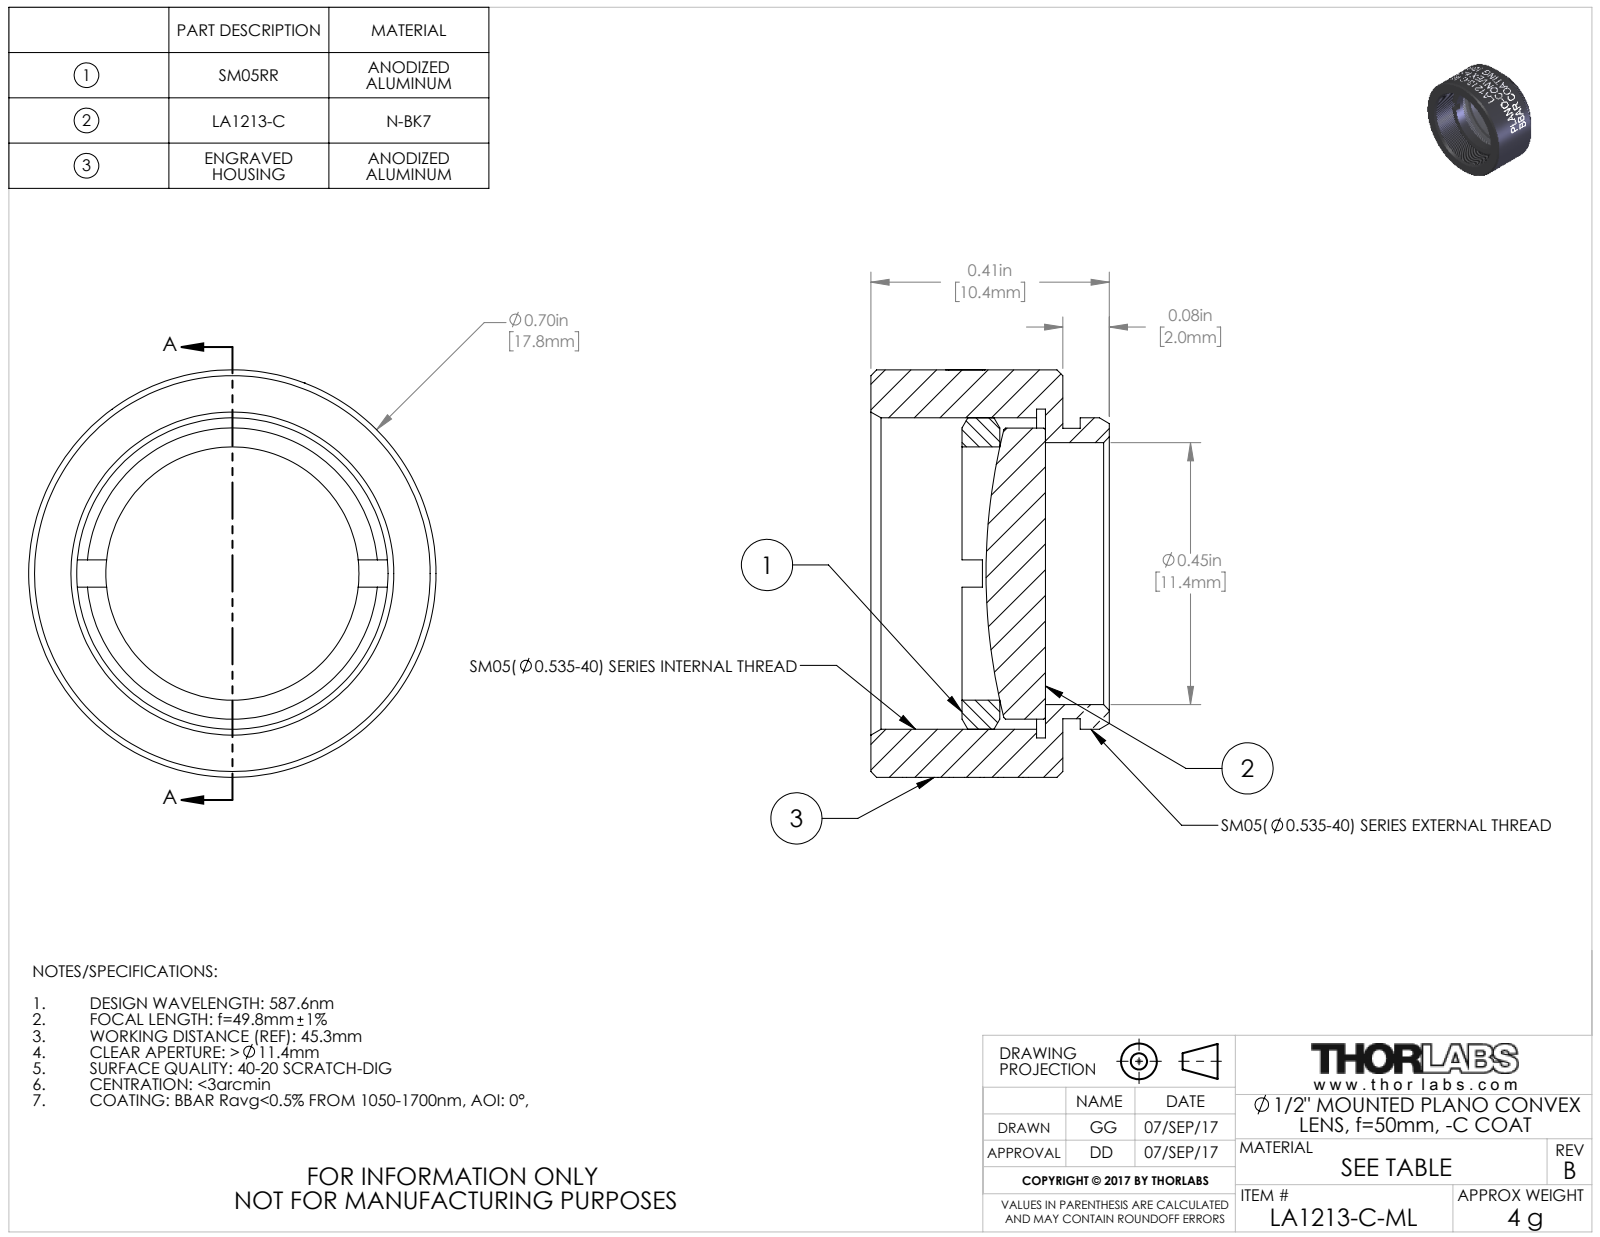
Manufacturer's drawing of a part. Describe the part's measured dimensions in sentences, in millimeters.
The part is named "24401-E0W". Its 3-D file was written by "SolidWorks 2016 (CONFIG_CONTROL_DESIGN)". It is 3 solids with 280 faces: 94 planar, 107 cylindrical and 79 other. Overall it measures 17.8 by 17.8 by 10.4 millimeters. Its volume is 1 300 cubic millimeters and its surface area 1 839 square millimeters. Round holes: 1 of diameter 11, 1 of diameter 11.4, 1 of diameter 13.6, 1 of diameter 14.4. Round bosses or shafts: 1 of diameter 17.8, 1 of diameter 13.6, 1 of diameter 12.7, 1 of diameter 12.7. Partial cylindrical surfaces (rounded edges, fillets, slot ends): 1 of radius 8.9. The main face-to-face distances are 0.8, 7.6, 8.4, 2.8, 2, 5.6, 4.4, 3.6, 1.7, 4.
